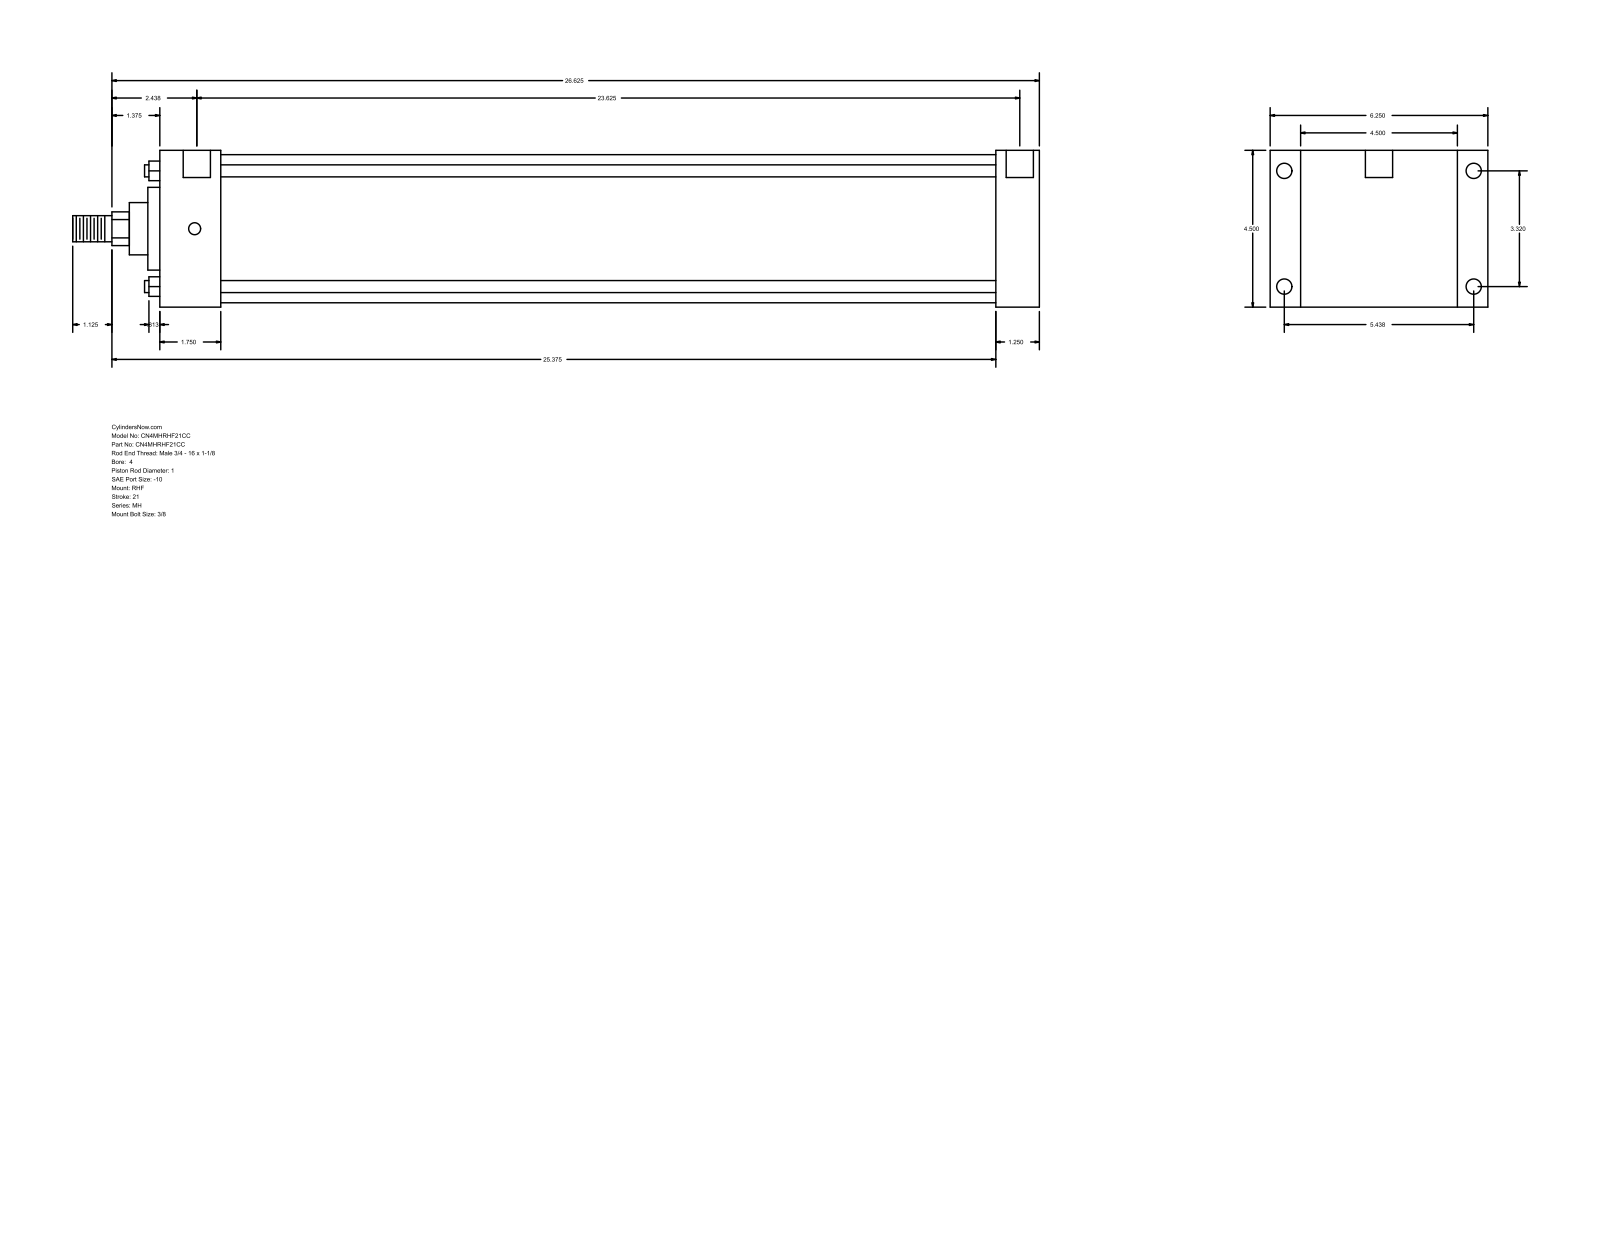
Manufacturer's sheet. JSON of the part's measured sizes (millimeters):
{"part_name": "MH_RHF__0400_1", "step_written_by": "GSSL Pune (CONFIG_CONTROL_DESIGN)", "units": "millimeters", "bodies": {"solids": 0, "faces": 90, "planar": 61, "cylindrical": 29, "other": 0}, "overall_size": [704.85, 158.75, 114.3], "round_holes": [[8.73, 4], [11.13, 4], [19.84, 2]], "round_bosses_or_shafts": [[8.76, 4], [107.95, 1], [60.33, 1], [38.1, 1], [25.4, 1], [19.05, 1]], "partial_cylinders_radius": [[12.29, 1]], "face_to_face_distances": [114.3, 641.35, 609.6, 31.75, 22.23, 136.53, 44.46, 565.14, 596.89, 158.76], "hole_center_spacings": [84.32, 138.12, 161.82, 603.25, 1.58, 1.59, 600.08, 601.66]}
